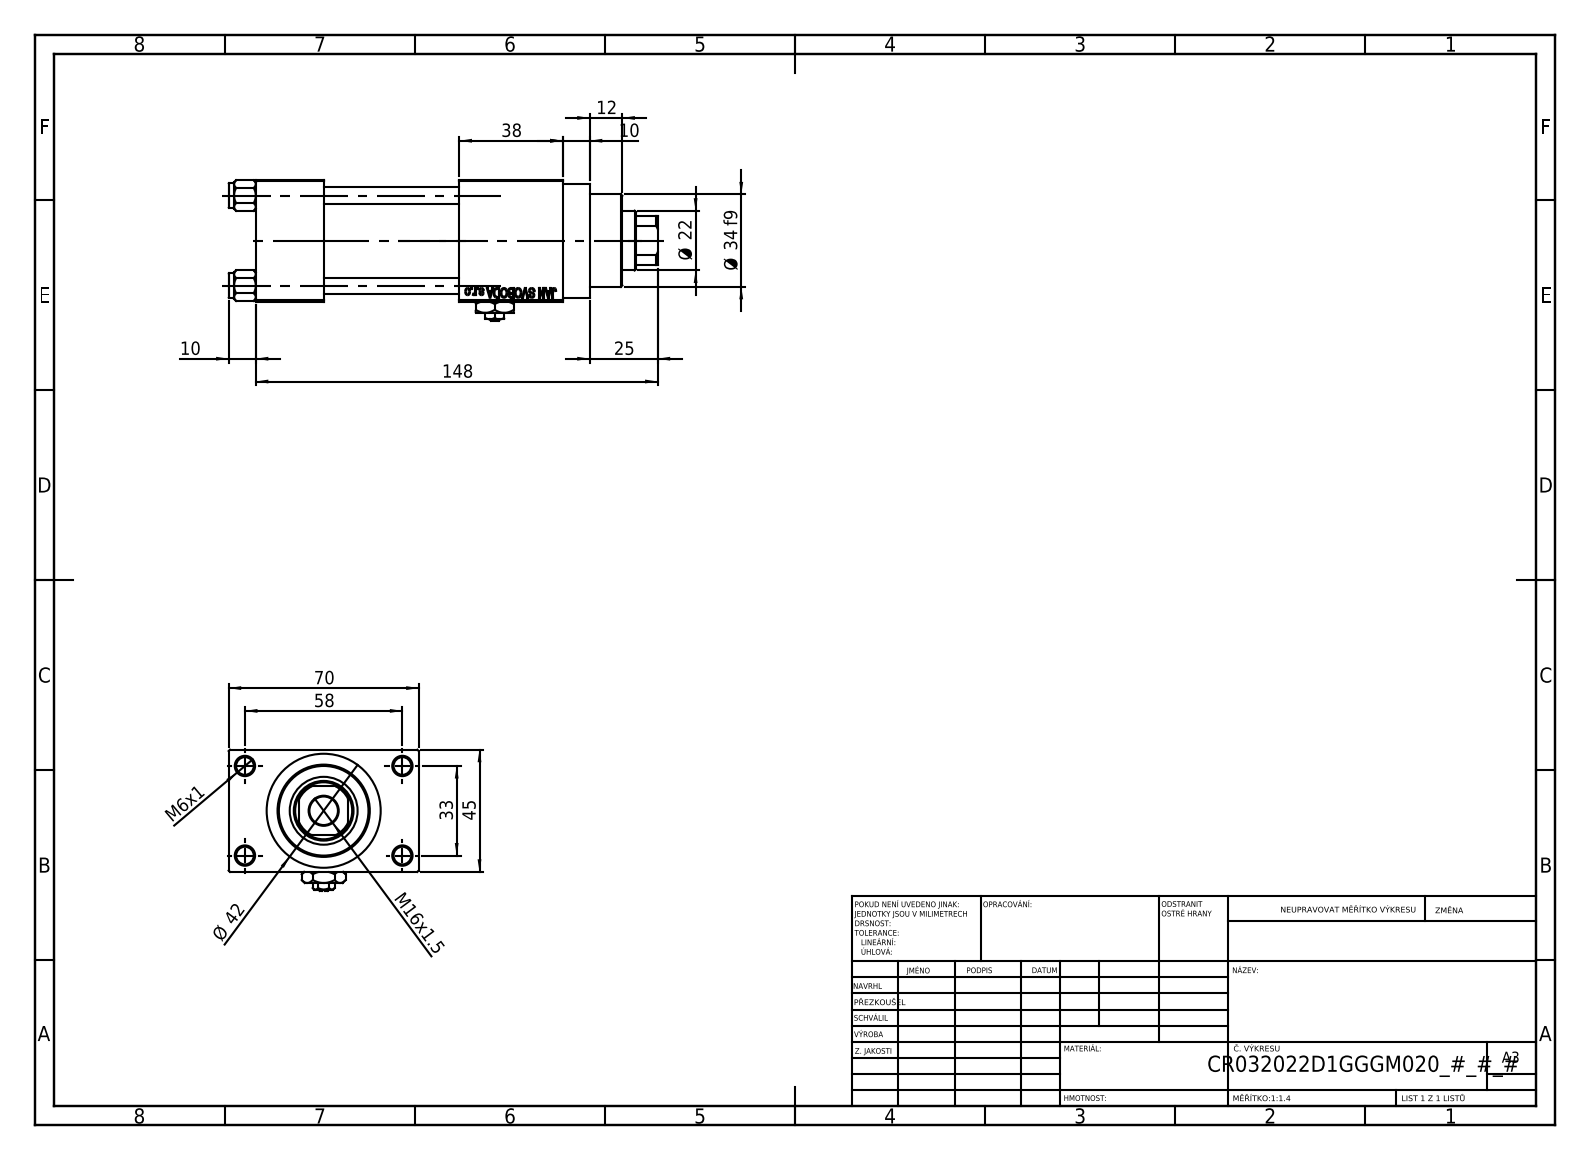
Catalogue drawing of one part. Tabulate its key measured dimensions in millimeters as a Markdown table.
| quantity | value |
| --- | --- |
| part name | Zatka_pro_OIL_PORT; V215CR_D_Body; V215CR_D_TYCINKA; V215CR_VCP_D (+2 more) |
| STEP written by | SolidWorks 2019 (CONFIG_CONTROL_DESIGN) |
| units | millimeters |
| bodies | 12 solids, 1150 faces (519 planar, 93 cylindrical, 538 other) |
| overall size | 158 × 70 × 52 |
| volume | 244 539 mm³ |
| surface area | 80 057 mm² |
| round holes (diameter × count) | 6 × 4, 6.5 × 4, 7 × 2, 13.16 × 2, 20 × 2, 10.5 × 1, 22 × 1, 24 × 1, 25 × 1, 32 × 1, 33 × 1 |
| round bosses / shafts (diameter × count) | 9 × 4, 42 × 1, 38 × 1, 34 × 1 |
| partial cylindrical surfaces (radius × count) | 10.5 × 1 |
| main face-to-face distances | 45, 25, 12.5, 57.5, 50, 75, 88, 70, 38, 113 |
| hole center spacings | 12.4, 23.48, 33.2, 33.37, 35.35, 45.6, 56.35, 33 |
